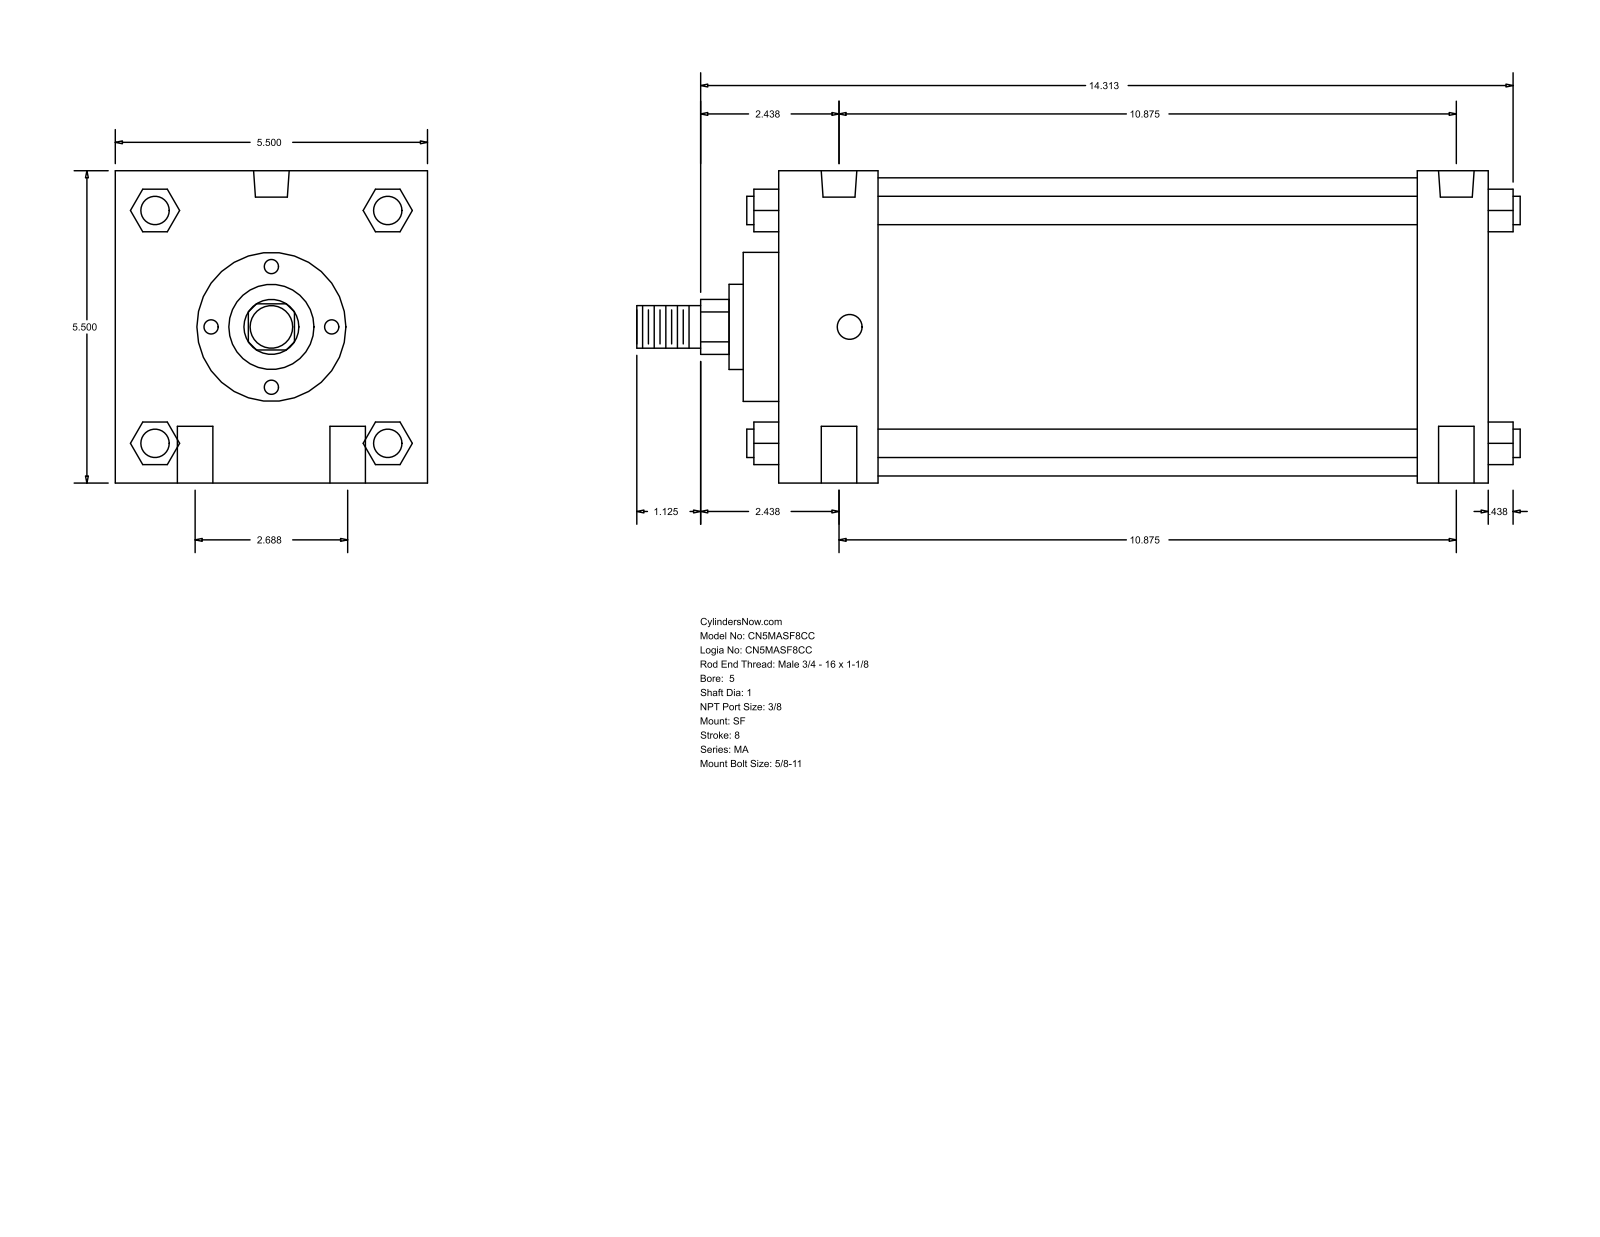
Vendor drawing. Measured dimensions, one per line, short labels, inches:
name: MA_SF__0500_1
written by: GSSL Pune (CONFIG_CONTROL_DESIGN)
unit: in
bodies: 0 solids, 126 faces (95 planar, 31 cylindrical, 0 other)
size: 15.563 × 5.5 × 5.5
holes: 4× ⌀0.625, 2× ⌀0.437, 2× ⌀0.627
bosses: 4× ⌀0.5, 1× ⌀5.25, 1× ⌀2.625, 1× ⌀1.5, 1× ⌀1, 1× ⌀0.75
rounds: 1× R0.484
face distances: 5.5, 12.5, 1.75, 11.25, 9.5, 10.75, 1.25, 0.625, 2.375, 11.875
hole spacings: 1.344, 10.958, 10.875, 2.687, 11.202, 10.5
